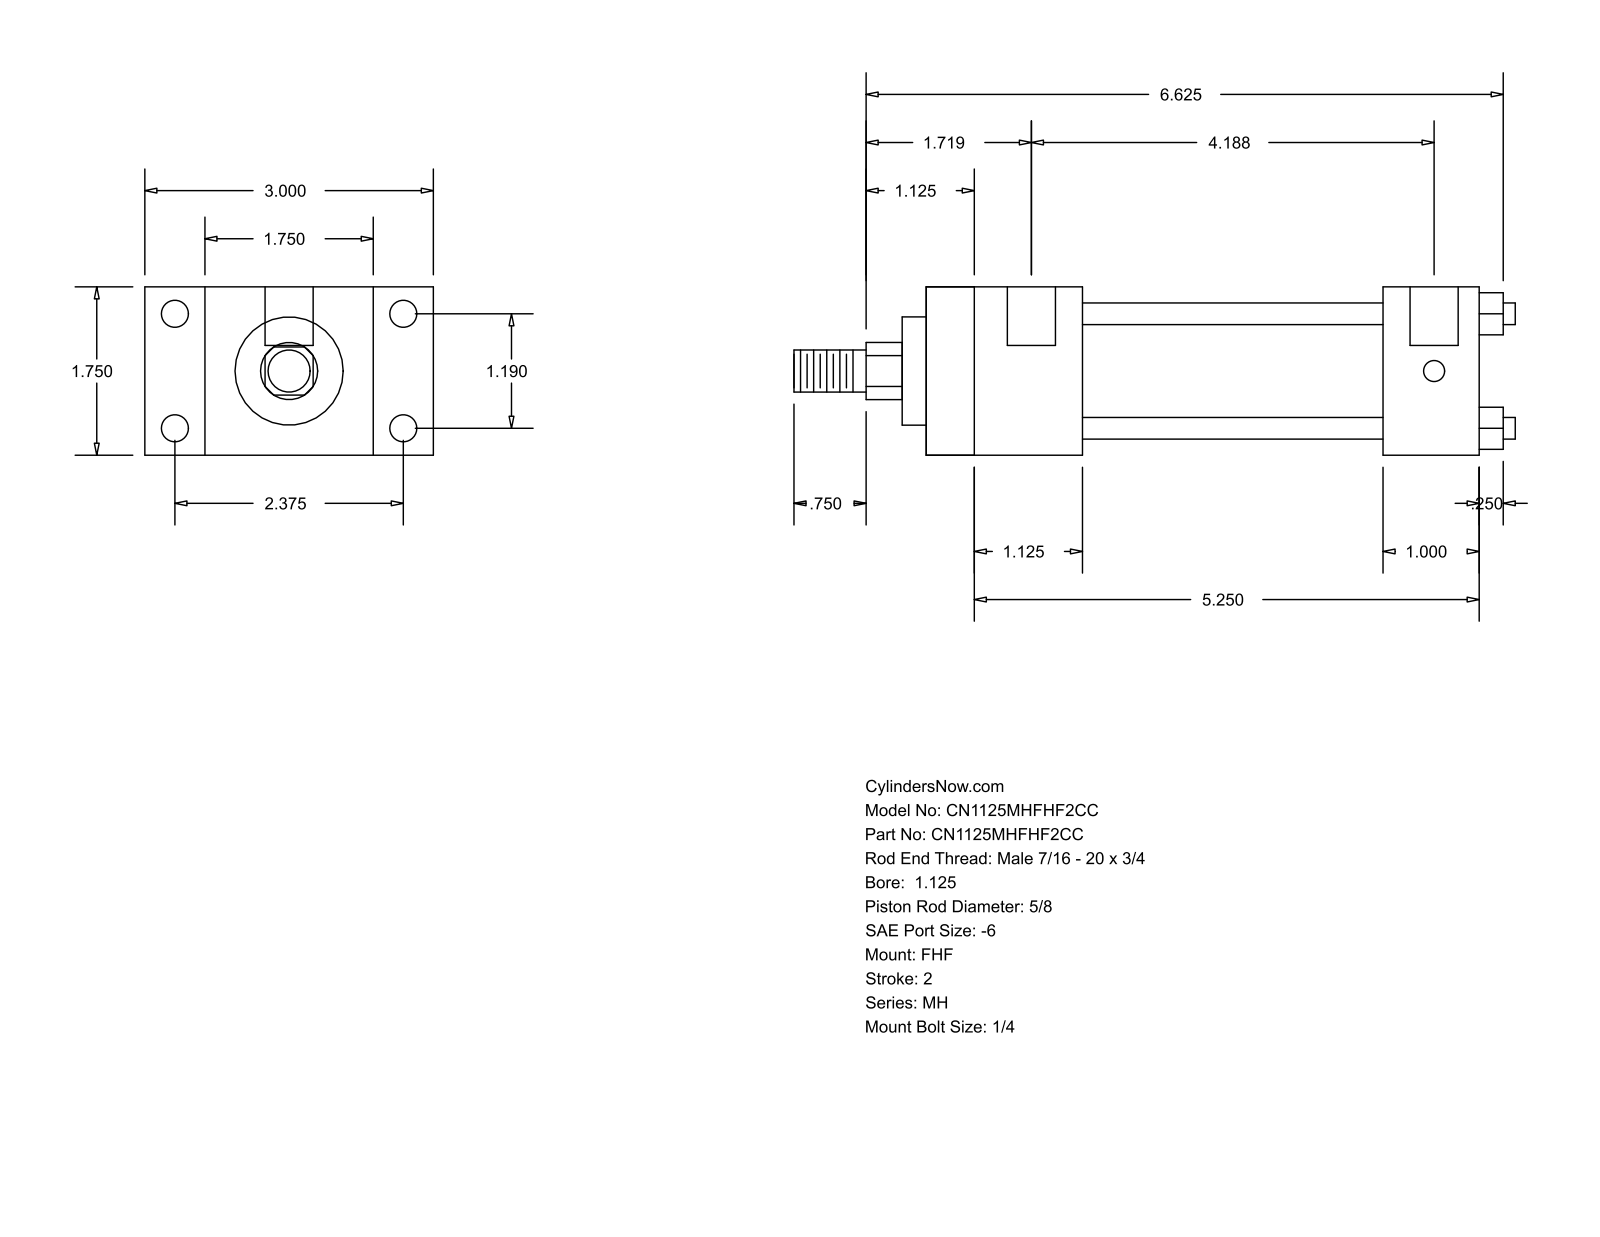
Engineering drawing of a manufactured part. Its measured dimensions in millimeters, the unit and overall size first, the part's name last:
Units: millimetres
Overall size (bounding box): 190.5 × 76.2 × 44.45
Round holes (diameter × count): ⌀5.56 ×4, ⌀7.14 ×4, ⌀12.7 ×2
Round bosses / shafts (diameter × count): ⌀5.71 ×4, ⌀34.92 ×1, ⌀28.57 ×1, ⌀15.88 ×1, ⌀11.11 ×1
Partial cylindrical surfaces — rounded edges, fillets, slot ends (radius × count): R7.54 ×1
Main face-to-face distances: 44.46, 15.87, 60.33, 41.27, 76.2, 146.05, 104.78, 25.4, 120.65, 79.38
Hole centre spacings: 30.22, 60.32, 67.47, 103.19, 3.17, 106.36
Bodies: 0 solids, 88 faces (60 planar, 28 cylindrical, 0 other)
Part name (STEP PRODUCT): MH_FHF__0112_0.625
STEP written by: GSSL Pune (CONFIG_CONTROL_DESIGN)
